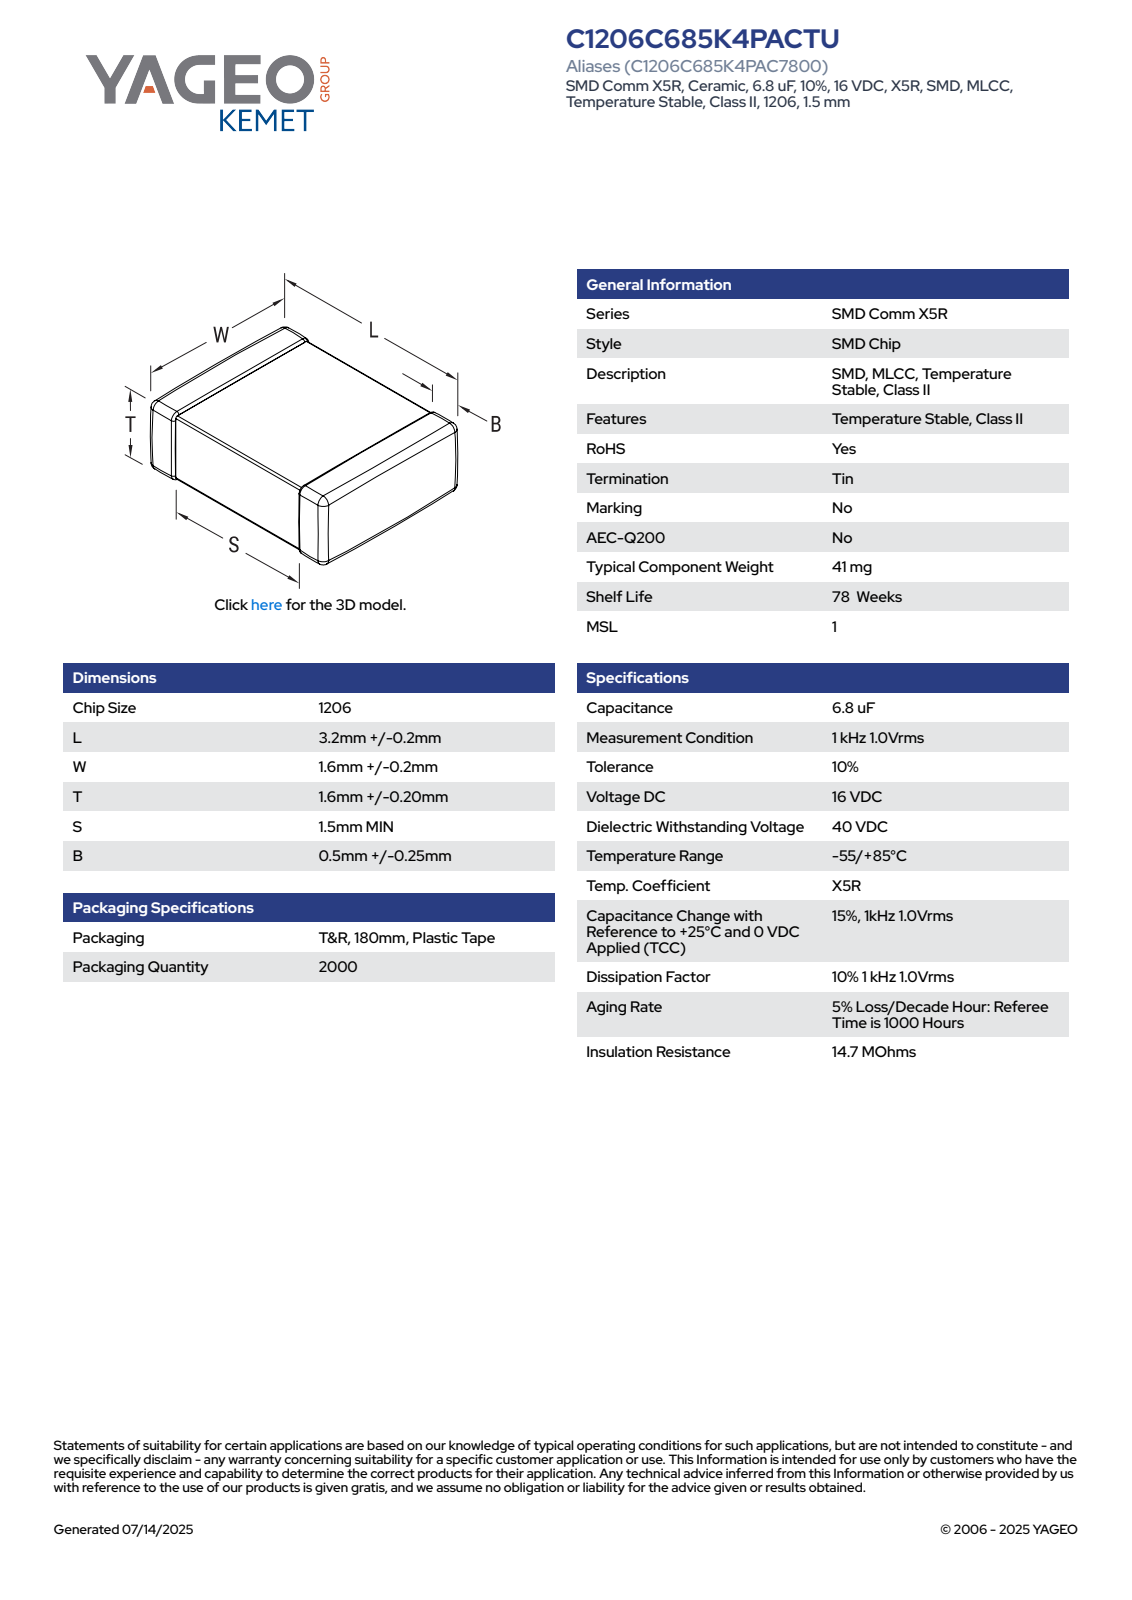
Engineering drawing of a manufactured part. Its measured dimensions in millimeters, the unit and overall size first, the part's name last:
Units: millimetres
Overall size (bounding box): 3.4 × 1.8 × 1.8
Main face-to-face distances: 1.76, 1.72, 1.8, 3.4, 1.77, 1.73, 0.99, 0.75, 0.77, 0.79
Volume: 11 mm³ · Surface area: 31 mm²
Bodies: 4 solids, 125 faces (71 planar, 38 cylindrical, 16 other)
Part name (STEP PRODUCT): CCS_CCSTDNOS_1206_L3.4W1.8T1.8B0.75
STEP written by: SolidWorks 2014 (AUTOMOTIVE_DESIGN)
